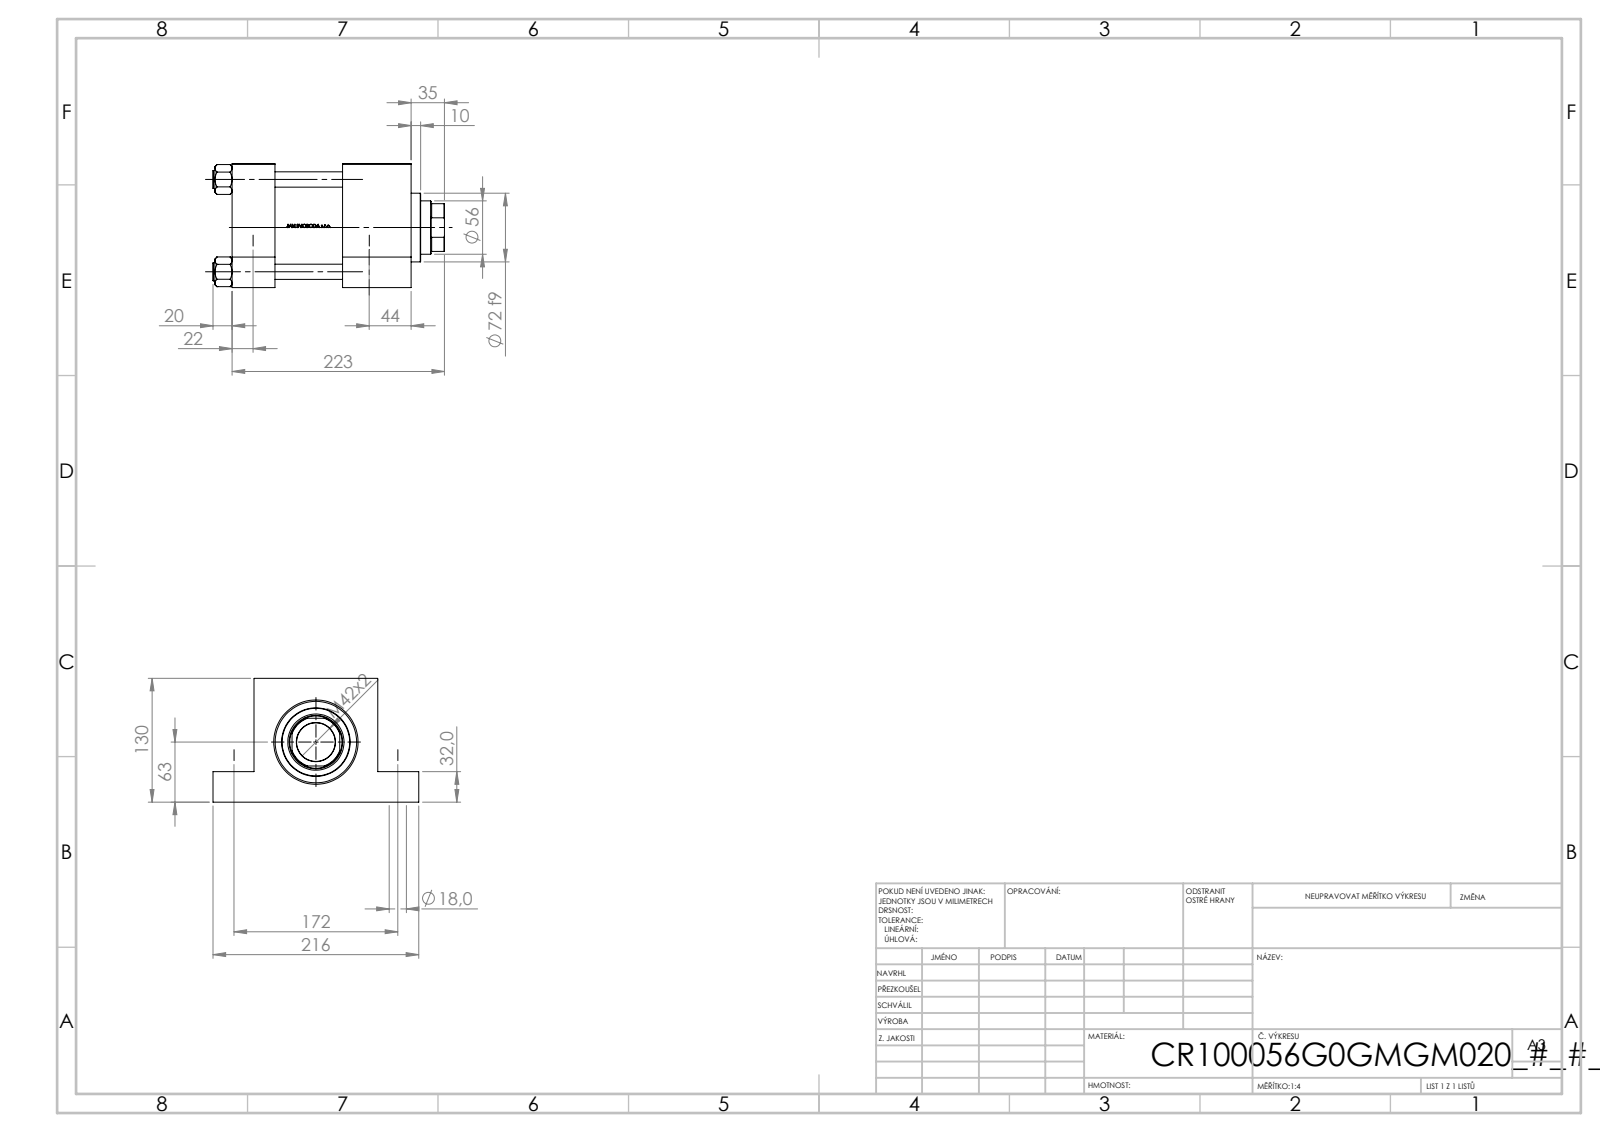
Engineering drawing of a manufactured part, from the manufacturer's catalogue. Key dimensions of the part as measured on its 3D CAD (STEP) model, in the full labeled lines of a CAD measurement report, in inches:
Part name (STEP PRODUCT): V215CR_G_TYCINKA; V215_VC_A; V215CR_G_Body; V215CR_VCP_G (+1 more)
STEP written by: SolidWorks 2019 (CONFIG_CONTROL_DESIGN)
Units: inches
Bodies: 15 solids, 1241 faces (524 planar, 137 cylindrical, 580 other)
Overall size (bounding box): 9.567 × 8.504 × 5.118
Volume: 172.6 in³ · Surface area: 600.6 in²
Round holes (diameter × count): ⌀0.63 ×4, ⌀1.024 ×4, ⌀0.276 ×2, ⌀1.041 ×2, ⌀1.378 ×2, ⌀1.594 ×1, ⌀2.205 ×1, ⌀2.323 ×1, ⌀2.992 ×1, ⌀3.366 ×1, ⌀3.937 ×1
Round bosses / shafts (diameter × count): ⌀0.748 ×4, ⌀4.173 ×1, ⌀2.835 ×1
Partial cylindrical surfaces — rounded edges, fillets, slot ends (radius × count): R1.063 ×1
Main face-to-face distances: 5.118, 1.772, 7.402, 5.63, 4.567, 2.795, 2.835, 1.26, 3.858, 1.693
Hole centre spacings: 2.698, 3.815, 4.803, 5.395, 6.772, 8.302, 4.665
